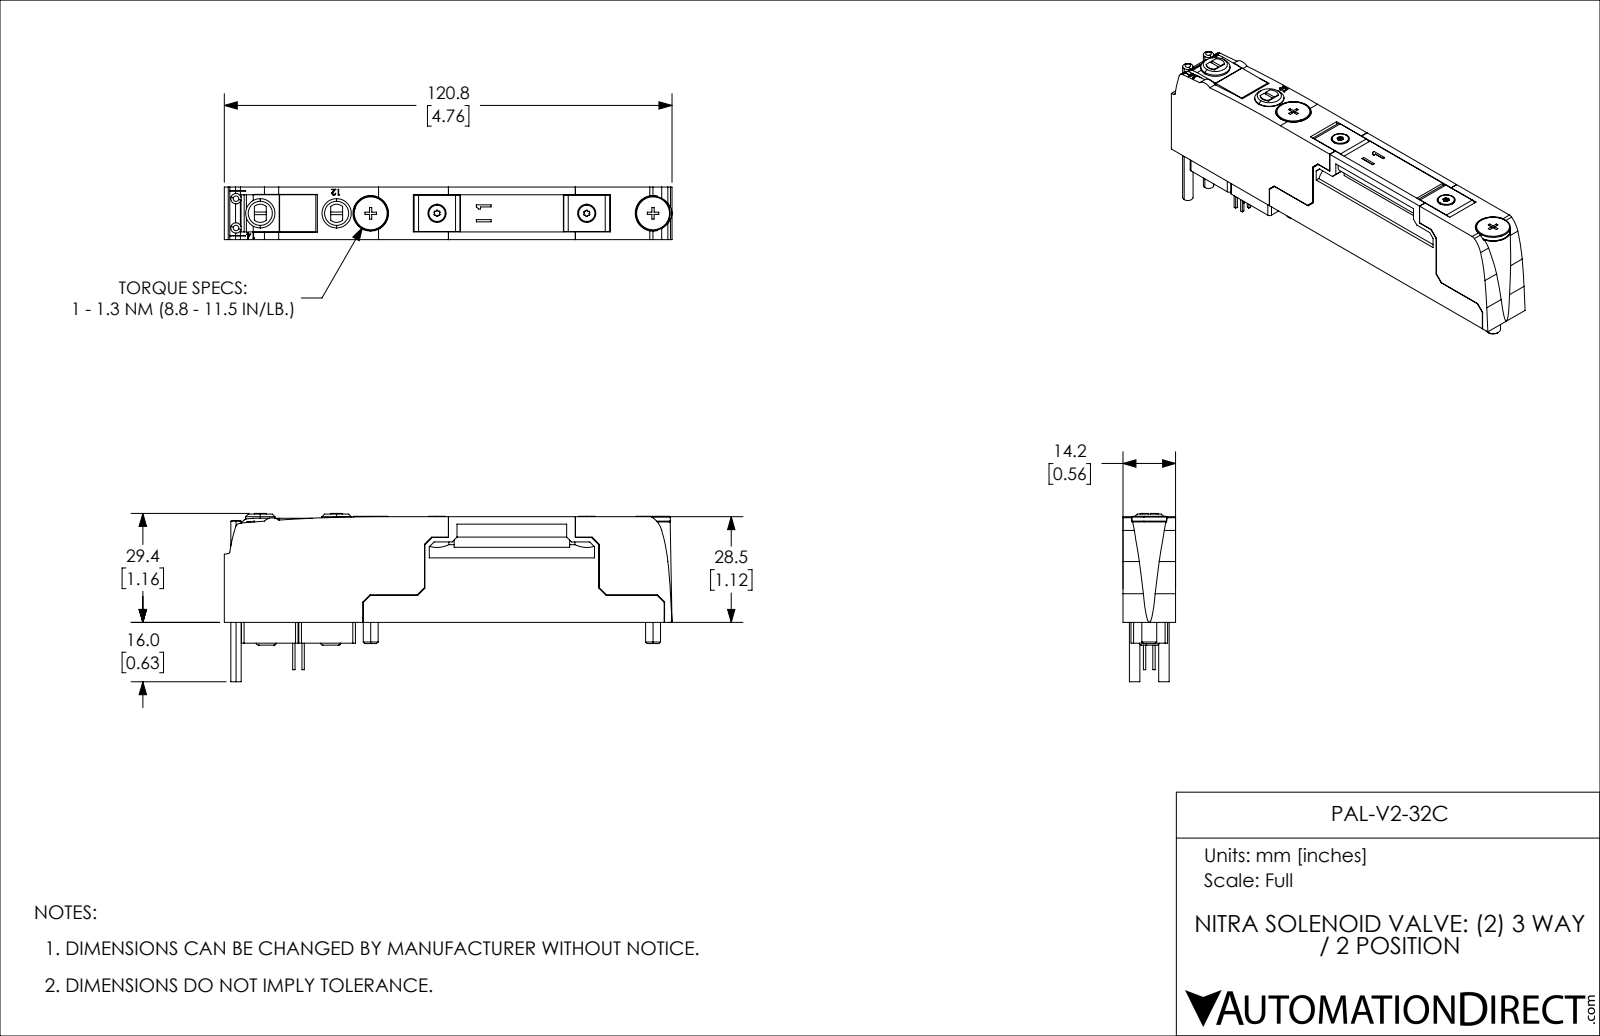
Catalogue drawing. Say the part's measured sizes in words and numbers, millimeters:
The part is named "PAL-V2-32C". Its 3-D file was written by "SolidWorks 2019 (CONFIG_CONTROL_DESIGN)". It is 1 solid with 553 faces: 395 planar, 121 cylindrical and 37 other. Overall it measures 120.8 by 45.4 by 14.2 millimeters. Its volume is 44 729 cubic millimeters and its surface area 18 020 square millimeters. Round holes: 2 of diameter 3.1, 2 of diameter 4.2, 1 of diameter 9.6. Round bosses or shafts: 2 of diameter 9.3, 2 of diameter 7.9, 2 of diameter 4.4, 2 of diameter 4, 2 of diameter 2.8. Partial cylindrical surfaces (rounded edges, fillets, slot ends): 8 of radius 0.7, 4 of radius 0.72, 4 of radius 1.2, 3 of radius 1.5, 2 of radius 0.65, 2 of radius 0.88, 2 of radius 1.95, 2 of radius 2.2. The main face-to-face distances are 14.2, 2.1, 12.1, 2.2, 6.4, 28.5, 17.2, 10, 5.6, 21.2. The hole center spacings are 10.8, 17.4, 28.2, 76.2, 87, 104.4.
